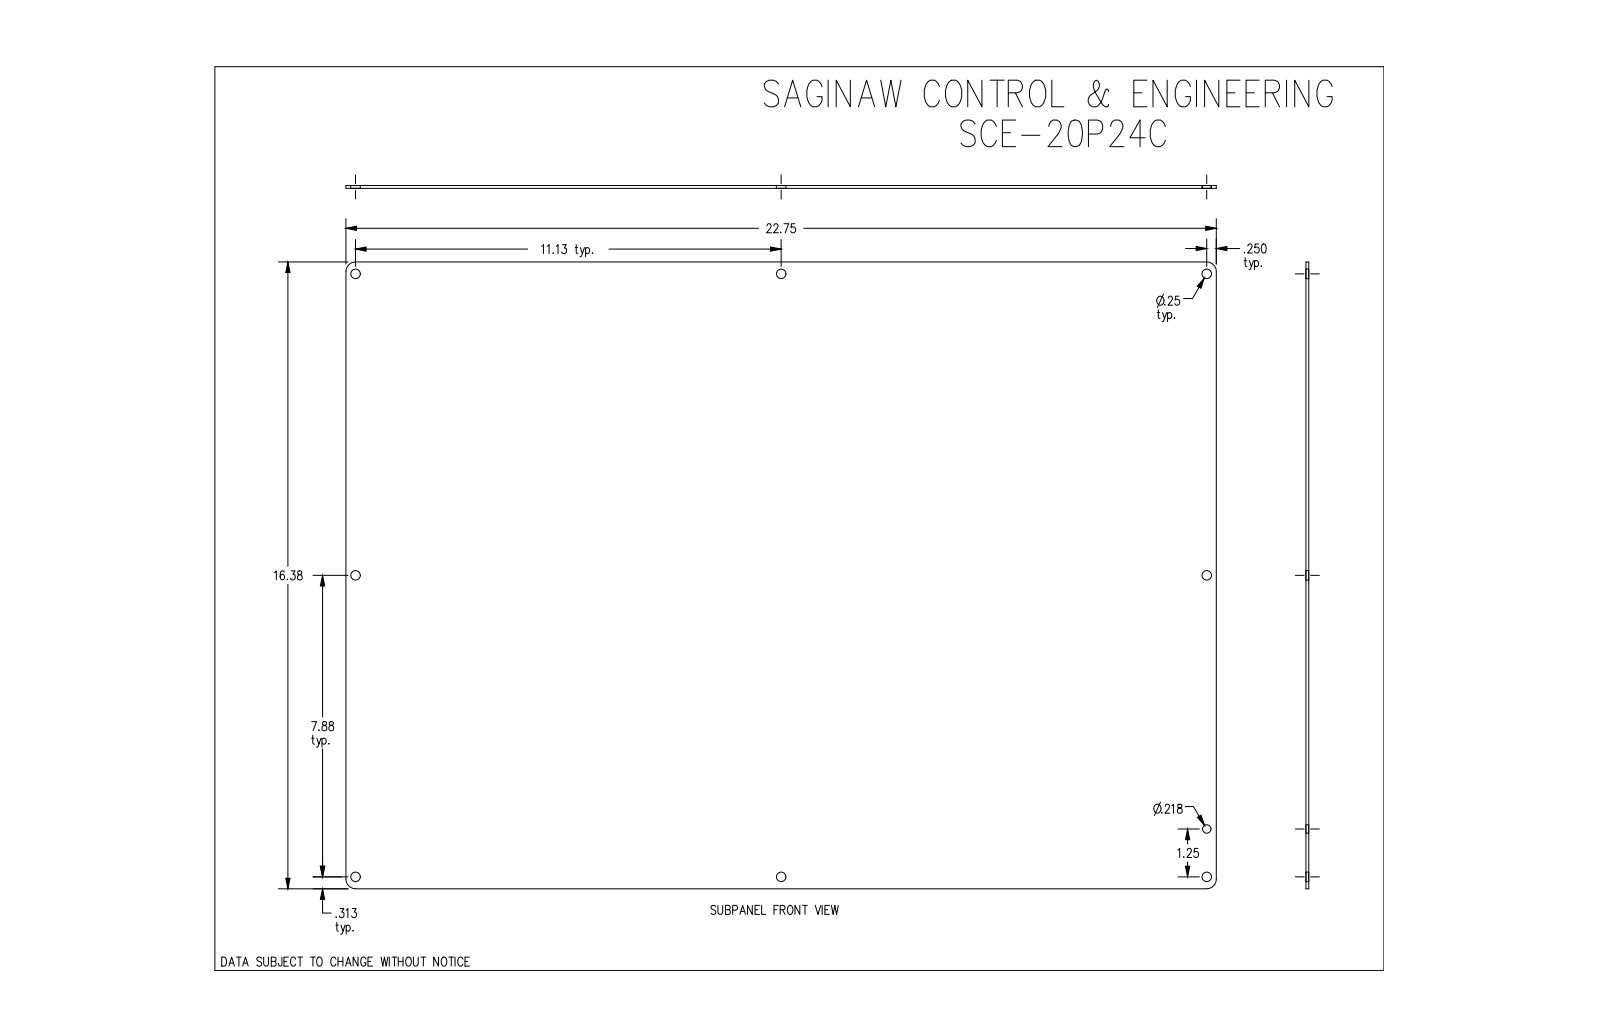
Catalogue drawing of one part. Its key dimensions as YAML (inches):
part_name: "SCE-20P24C"
step_written_by: "SolidWorks 2019 (CONFIG_CONTROL_DESIGN)"
units: inches
bodies: {solids: 1, faces: 19, planar: 6, cylindrical: 13, other: 0}
overall_size: [22.75, 16.375, 0.075]
volume: 27.9
surface_area: 750.5
round_holes:
  - {diameter: 0.25, count: 8}
  - {diameter: 0.218, count: 1}
partial_cylinders:
  - {radius: 0.25, count: 4}
face_to_face_distances: [0.075, 16.375, 22.75]
hole_center_spacings: [7.875, 11.125, 13.63, 19.282, 23.602, 15.75, 22.25, 27.26]
